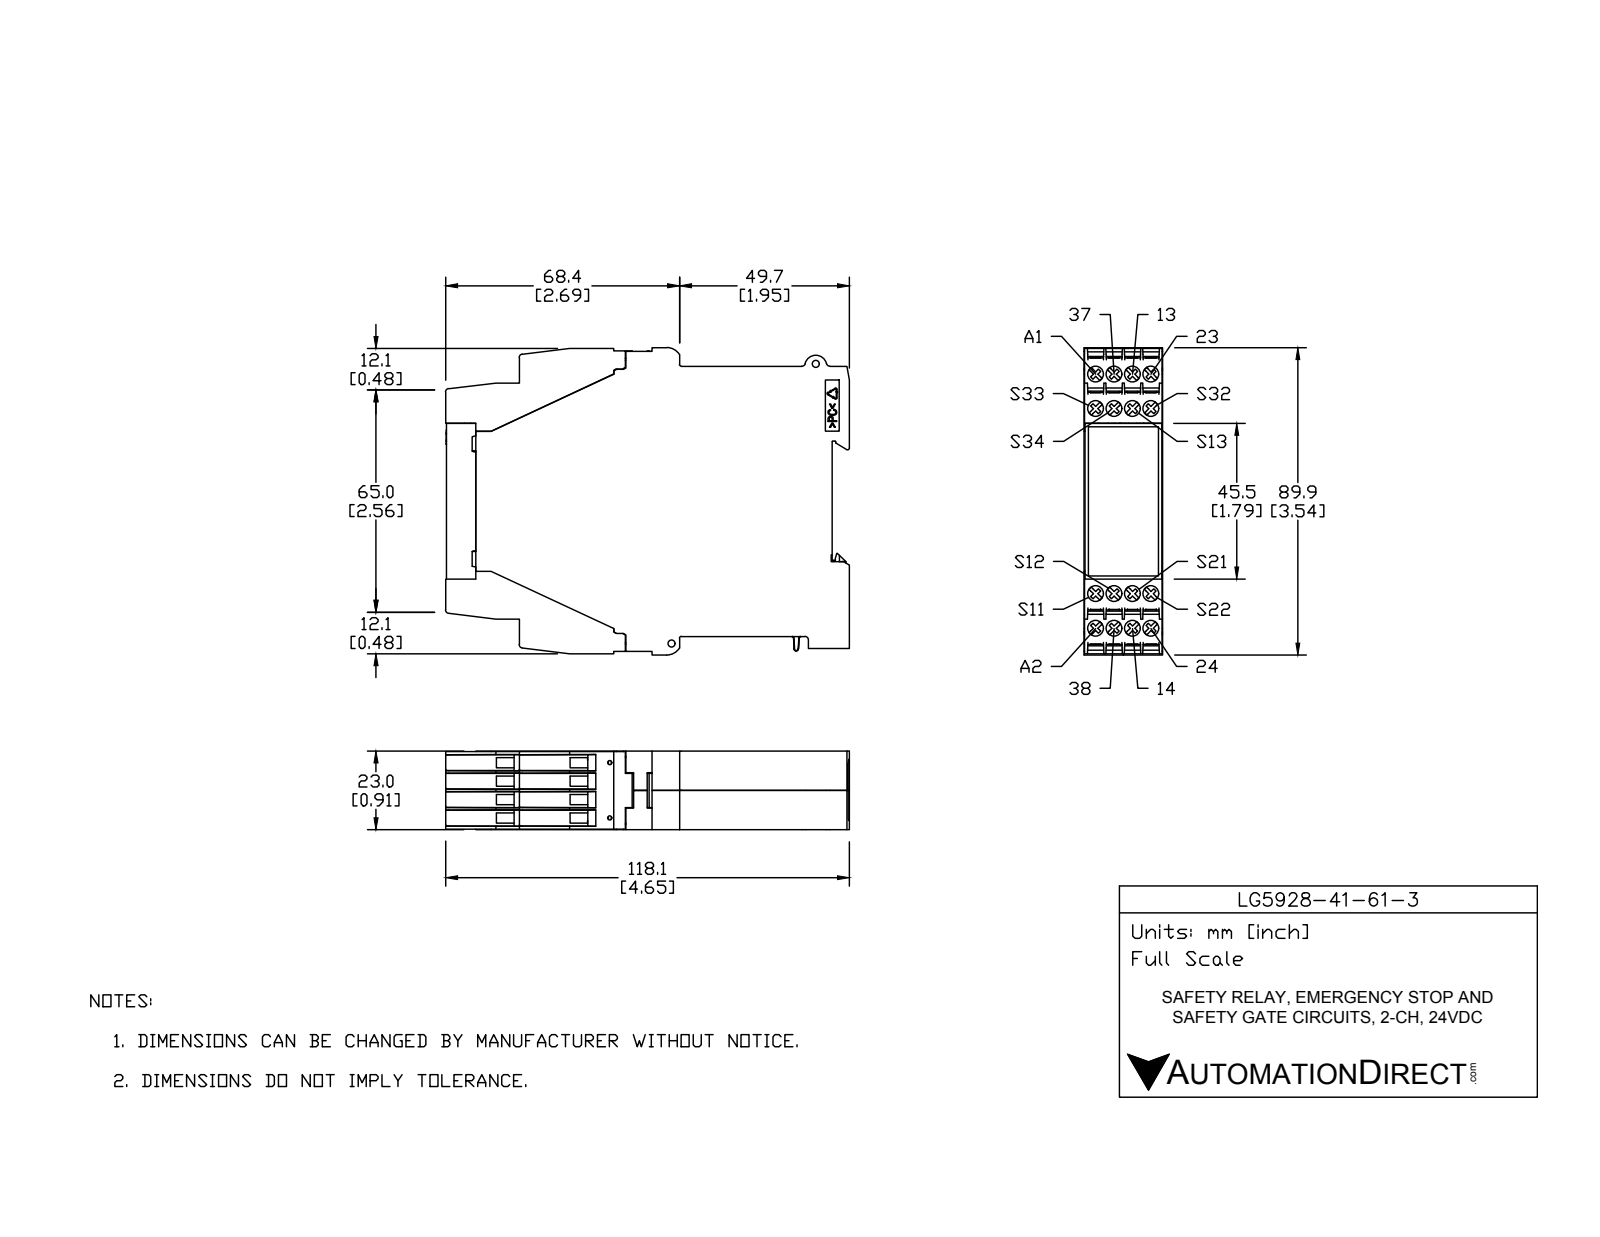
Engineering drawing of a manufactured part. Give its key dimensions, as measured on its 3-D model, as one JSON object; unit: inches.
{"part_name": "LG5928-41-61-3", "step_written_by": "SolidWorks 2017 (AUTOMOTIVE_DESIGN)", "units": "inches", "bodies": {"solids": 1, "faces": 2054, "planar": 1604, "cylindrical": 319, "other": 131}, "overall_size": [4.656, 3.537, 0.906], "volume_in3": 12.64, "surface_area_in2": 62.74, "round_holes": [[0.181, 16], [0.079, 3], [0.047, 2], [0.079, 2]], "round_bosses_or_shafts": [[0.173, 16], [0.087, 1]], "partial_cylinders_radius": [[0.008, 52], [0.012, 36], [0.02, 31], [0.039, 28], [0.006, 6], [0.014, 6], [0.174, 2], [0.043, 1]], "face_to_face_distances": [0.906, 0.897, 0.894, 0.902, 4.451, 0.031, 0.874, 0.03, 0.039, 3.11], "hole_center_spacings": [0.213, 0.451, 2.541, 0.398, 0.425, 0.582, 2.531, 2.567]}
